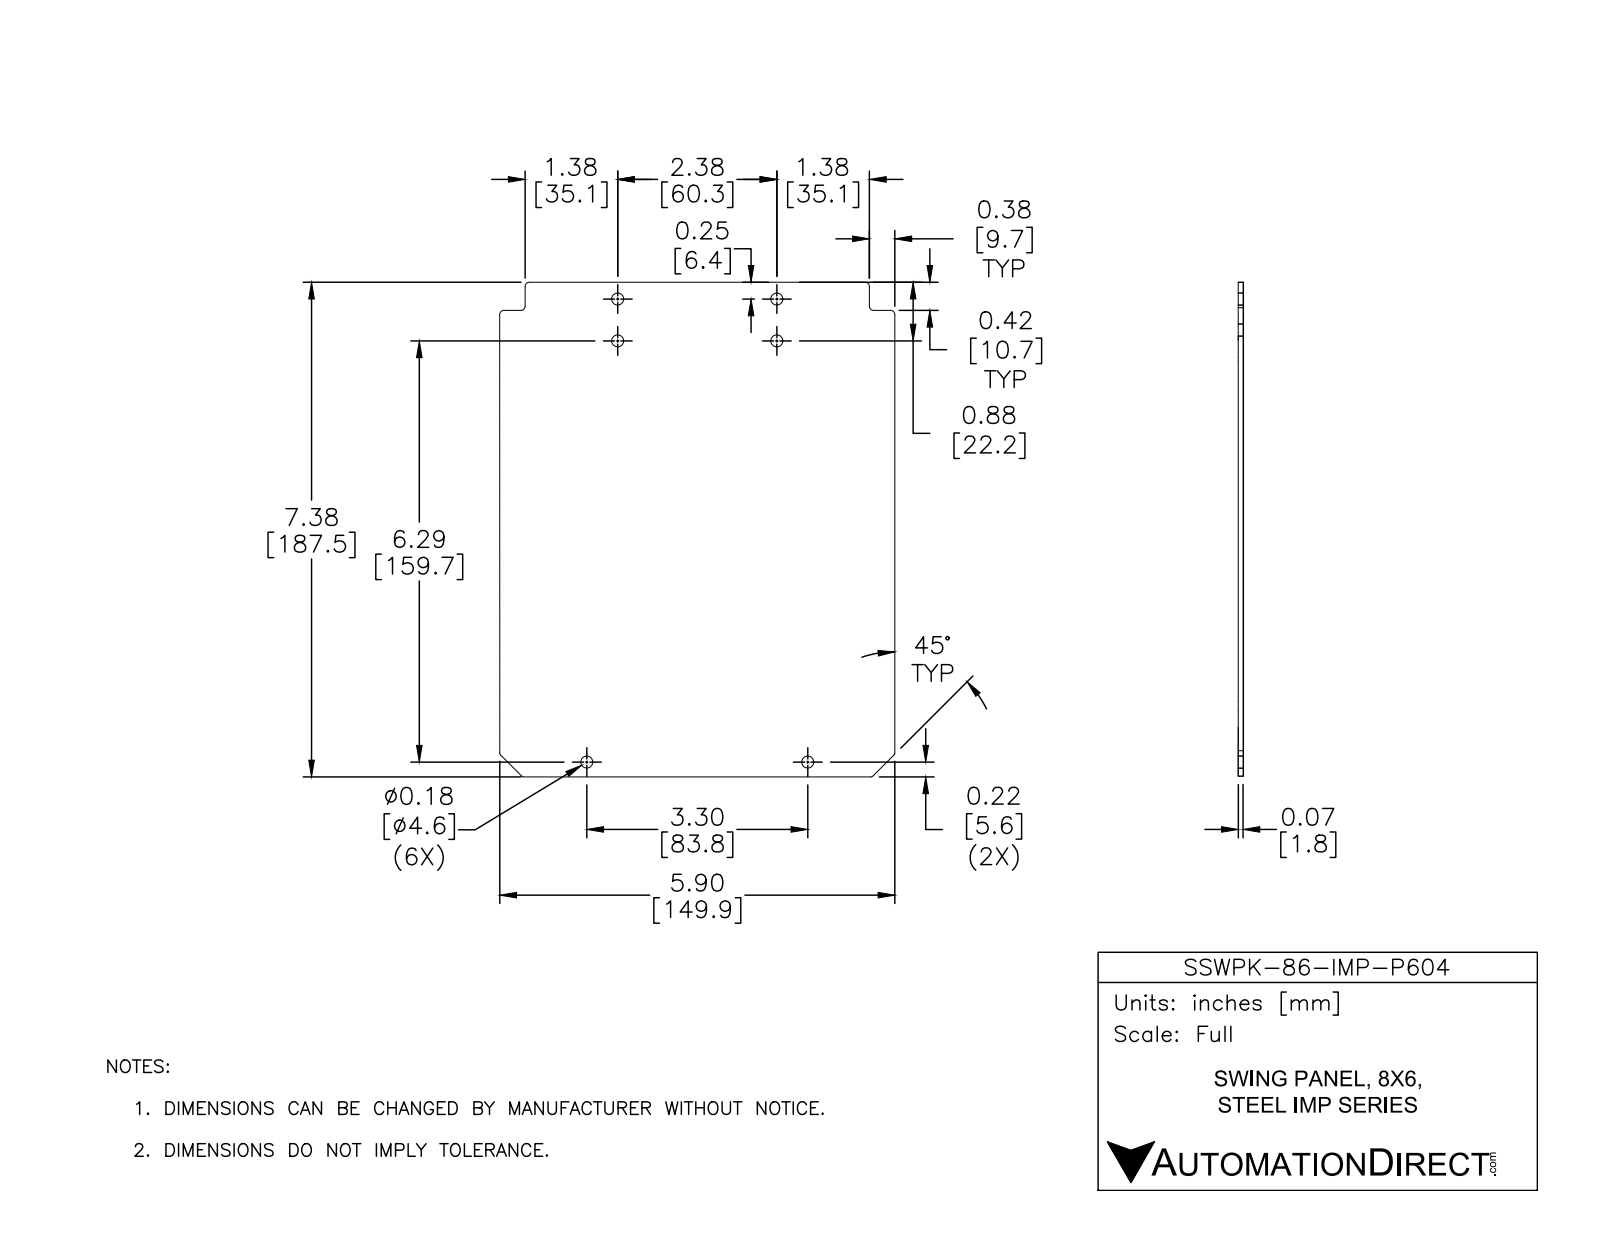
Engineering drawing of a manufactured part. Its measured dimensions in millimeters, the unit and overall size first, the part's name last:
Units: millimetres
Overall size (bounding box): 187.5 × 149.9 × 1.6
Round holes (diameter × count): ⌀4.6 ×6
Partial cylindrical surfaces — rounded edges, fillets, slot ends (radius × count): R1.6 ×6, R1 ×2, R1 ×1, R1 ×1
Main face-to-face distances: 1.6, 149.9, 187.5, 176.9, 10.7, 140.2, 9.7, 9.7, 130.6, 140.2
Hole centre spacings: 15.9, 60.3, 62.4, 160.1, 175.2, 176, 189.8, 83.8
Volume: 45 130 mm³ · Surface area: 56 660 mm²
Bodies: 1 solid, 34 faces (12 planar, 22 cylindrical, 0 other)
Part name (STEP PRODUCT): SSWPK-86-IMP-P604
STEP written by: SolidWorks 2016 (AUTOMOTIVE_DESIGN)
